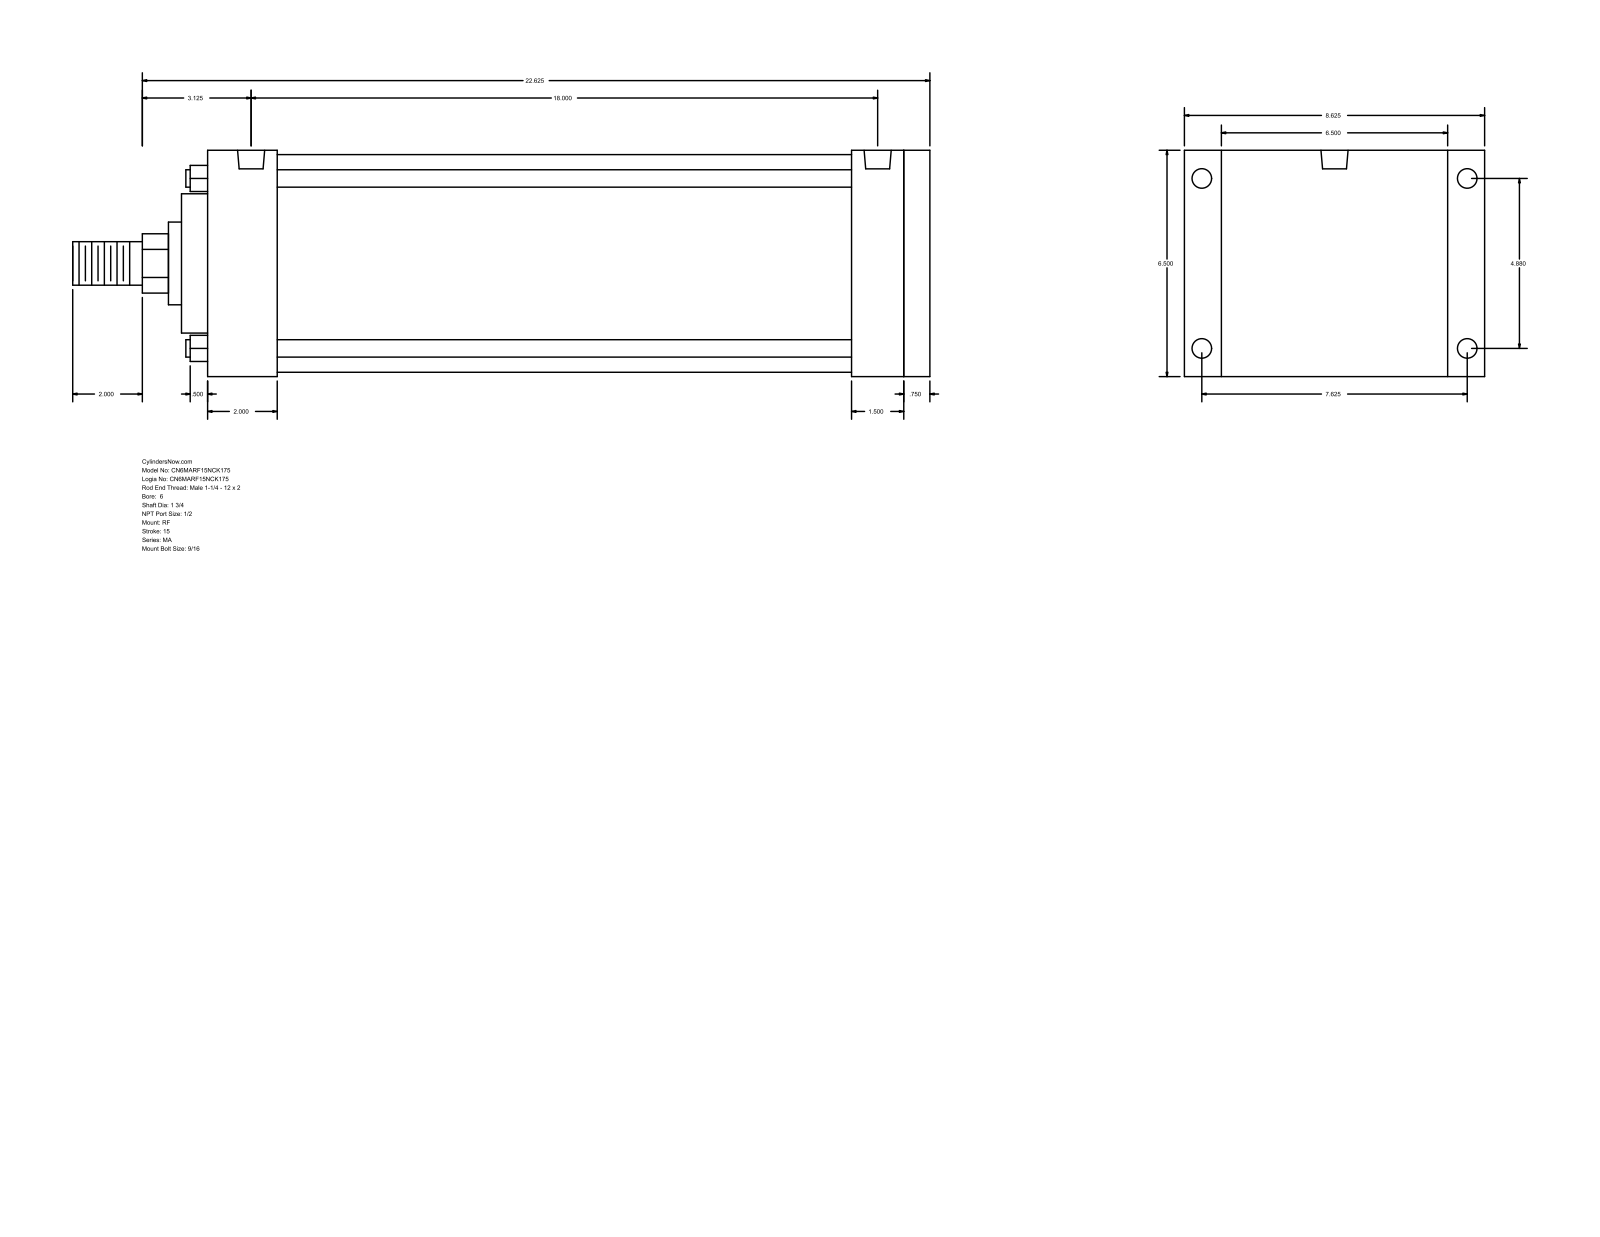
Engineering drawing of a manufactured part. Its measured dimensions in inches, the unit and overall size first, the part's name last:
Units: inches
Overall size (bounding box): 24.625 × 8.625 × 6.5
Round holes (diameter × count): ⌀0.563 ×4, ⌀0.687 ×4, ⌀0.778 ×2
Round bosses / shafts (diameter × count): ⌀0.5 ×4, ⌀6.25 ×1, ⌀4 ×1, ⌀2.375 ×1, ⌀1.75 ×1, ⌀1.25 ×1
Partial cylindrical surfaces — rounded edges, fillets, slot ends (radius × count): R0.852 ×1
Main face-to-face distances: 6.5, 20.75, 0.75, 20, 1.5, 2, 18, 18.75, 18.5, 16.5
Hole centre spacings: 4.88, 7.625, 9.053, 18
Bodies: 0 solids, 94 faces (65 planar, 29 cylindrical, 0 other)
Part name (STEP PRODUCT): MA_RF__0600_1.75
STEP written by: GSSL Pune (CONFIG_CONTROL_DESIGN)
